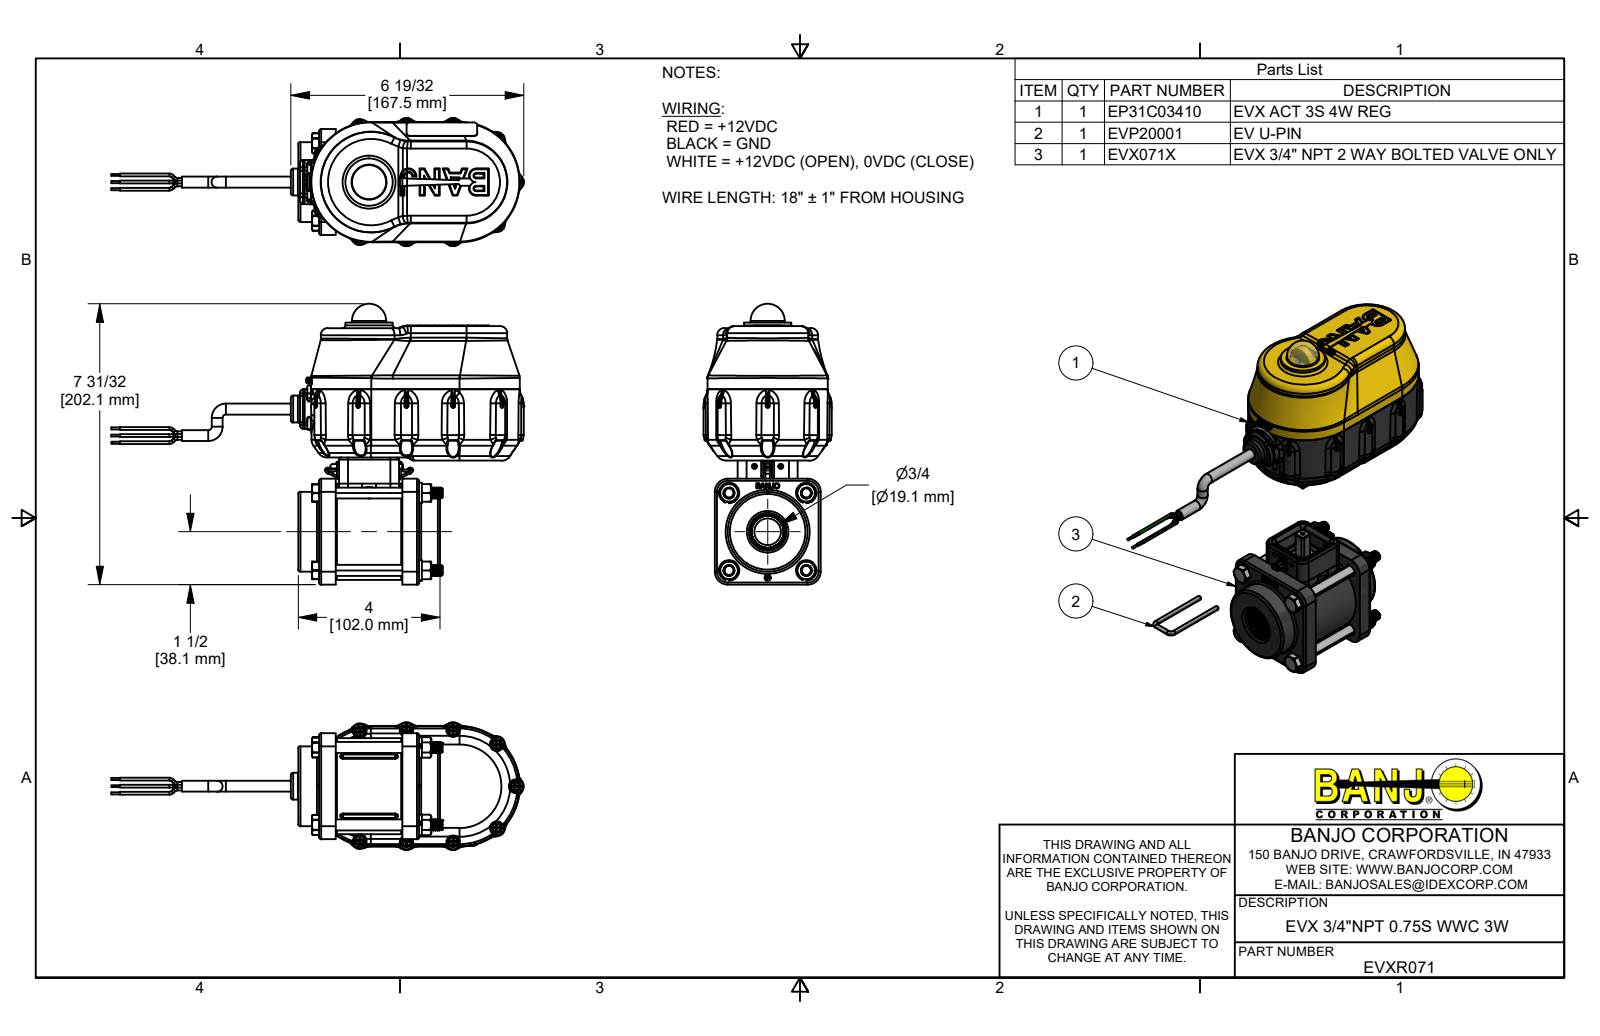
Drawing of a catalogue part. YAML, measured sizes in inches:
part_name: "EVXR071; EP31C03410; 91400A119; 95584A200 (+8 more)"
step_written_by: "Autodesk Inventor 2021 (AUTOMOTIVE_DESIGN)"
units: inches
bodies: {solids: 95, faces: 12875, planar: 3675, cylindrical: 3449, other: 5751}
overall_size: [11.685, 7.957, 3.63]
volume: 51.56
surface_area: 576.3
round_holes:
  - {diameter: 0.15, count: 13}
  - {diameter: 0.095, count: 11}
  - {diameter: 0.107, count: 4}
  - {diameter: 0.126, count: 4}
  - {diameter: 0.135, count: 4}
  - {diameter: 0.136, count: 4}
  - {diameter: 0.17, count: 4}
  - {diameter: 0.252, count: 4}
  - {diameter: 0.322, count: 4}
  - {diameter: 0.365, count: 4}
  - {diameter: 1.02, count: 3}
  - {diameter: 0.089, count: 2}
round_bosses_or_shafts:
  - {diameter: 0.268, count: 60}
  - {diameter: 0.08, count: 20}
  - {diameter: 0.25, count: 17}
  - {diameter: 0.14, count: 11}
  - {diameter: 0.108, count: 11}
  - {diameter: 0.085, count: 11}
  - {diameter: 0.058, count: 8}
  - {diameter: 0.313, count: 5}
partial_cylinders:
  - {radius: 0.04, count: 147}
  - {radius: 0.02, count: 83}
  - {radius: 0.06, count: 62}
  - {radius: 0.01, count: 56}
  - {radius: 0.005, count: 45}
  - {radius: 0.03, count: 34}
  - {radius: 0.08, count: 28}
  - {radius: 0.125, count: 24}
face_to_face_distances: [0.1, 2.565, 2.95, 1.685, 2.465, 0.78, 0.055, 0.125, 0.165, 0.88]
hole_center_spacings: [2.192, 1.046, 1.283, 1.55, 1.662, 1.891, 3.176, 3.296]
